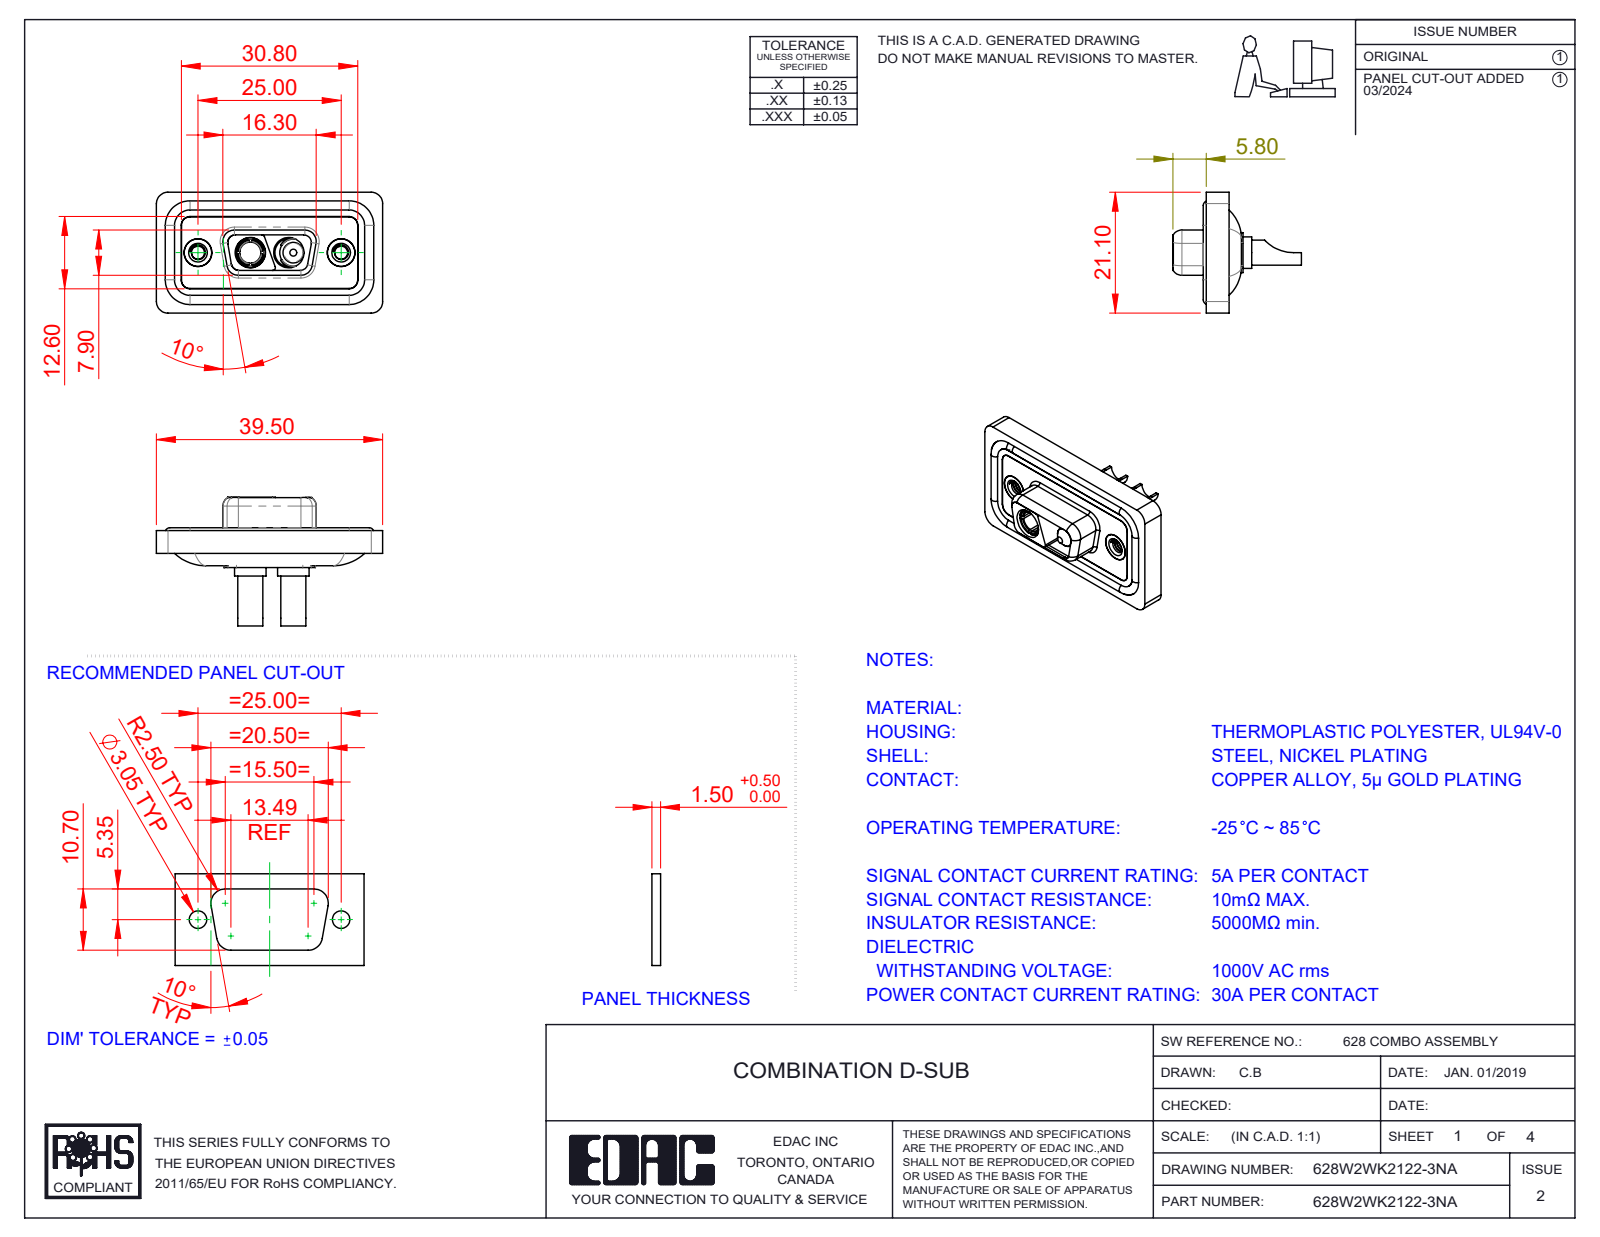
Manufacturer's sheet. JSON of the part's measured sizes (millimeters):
{"part_name": "628Combo Waterproof Housing_09 Contacts; 628Combo Shell Front_09 Contacts; 628W2WK2122-3NA; 628Combo Shell Rear_09 Contacts (+4 more)", "step_written_by": "SolidWorks 2023 (CONFIG_CONTROL_DESIGN)", "units": "millimeters", "bodies": {"solids": 11, "faces": 510, "planar": 150, "cylindrical": 239, "other": 121}, "overall_size": [39.5, 22.45, 21.1], "volume_mm3": 4653, "surface_area_mm2": 7556, "round_holes": [[4.85, 4], [2.26, 2], [3.5, 2], [4, 2], [4.05, 2], [5, 2], [5.3, 2], [3.7, 1]], "round_bosses_or_shafts": [[1.6, 4], [5.5, 2], [5.2, 2], [4.95, 2], [4.8, 2], [4.75, 2], [4.4, 2], [3.75, 2]], "partial_cylinders_radius": [[1.5, 22], [2, 18], [1.35, 8], [1.6, 8], [0.5, 6], [0.25, 4], [0.6, 4], [0.65, 4]], "face_to_face_distances": [0.4, 1.1, 2.9, 1.6, 0.5, 1.8, 5.65, 5.35, 3.1, 0.7], "hole_center_spacings": [9.14, 15.86, 6.72, 25]}
